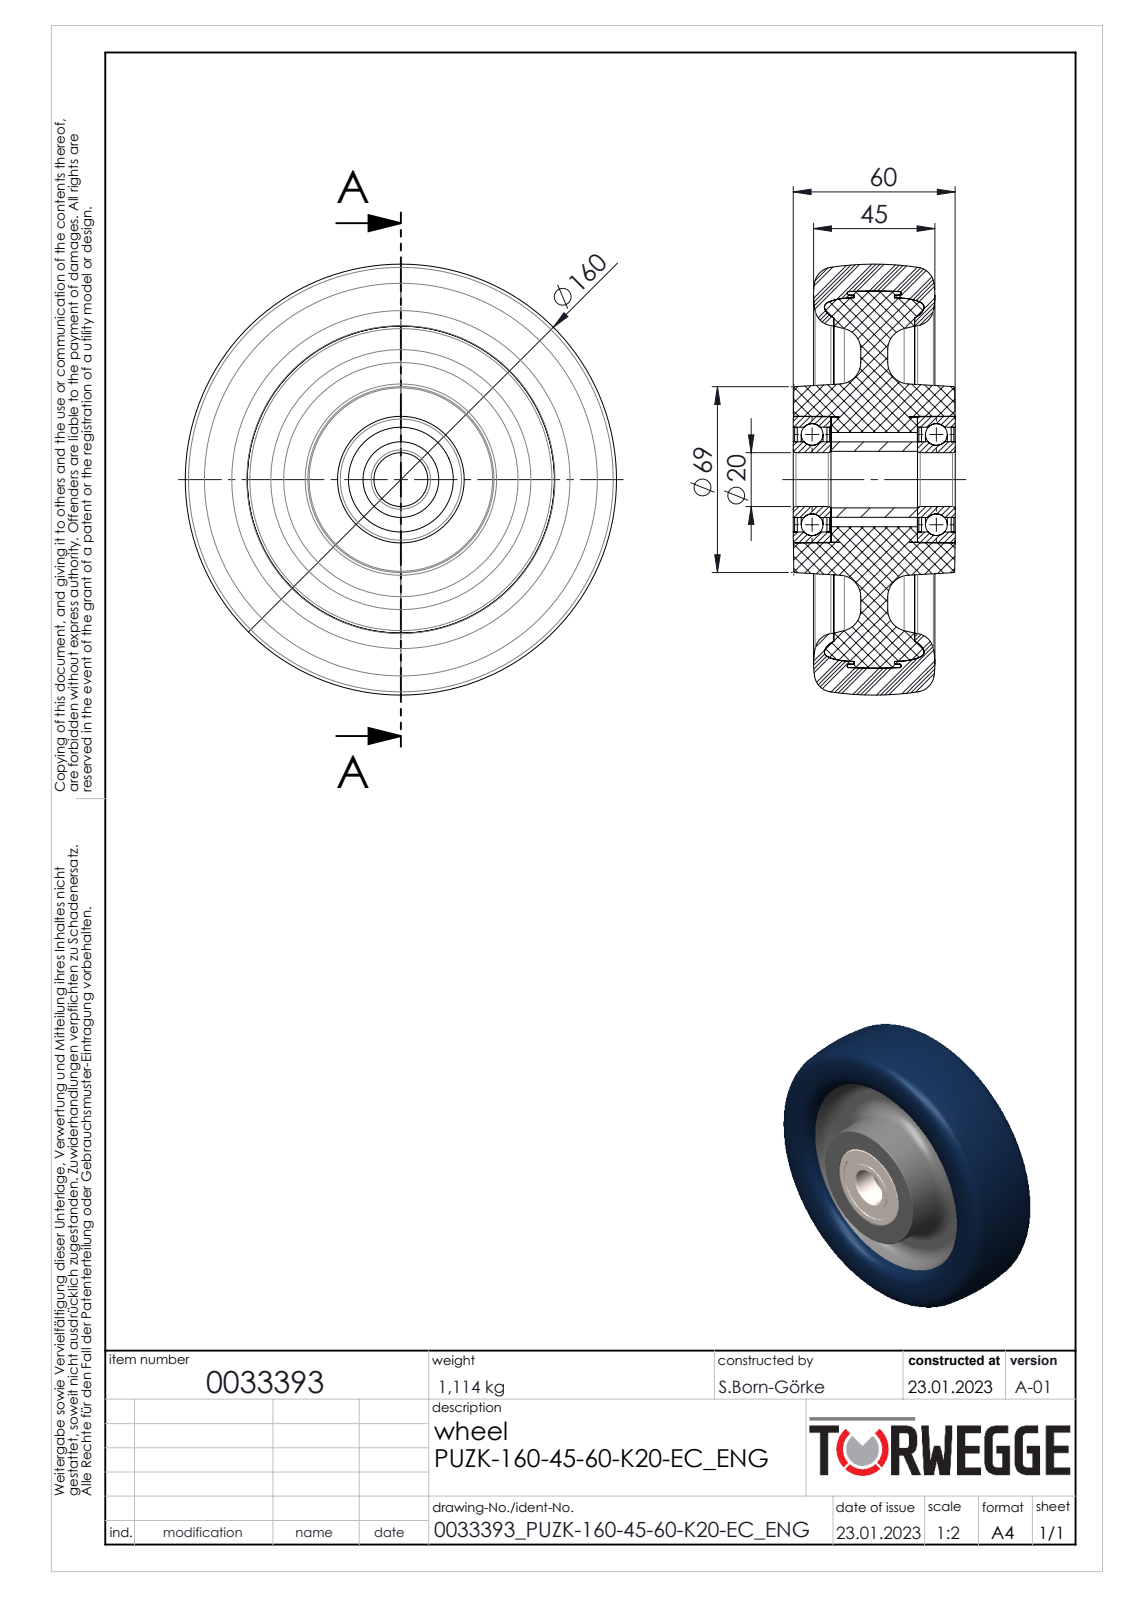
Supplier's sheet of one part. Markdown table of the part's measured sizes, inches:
| quantity | value |
| --- | --- |
| part name | 0033393 |
| STEP written by | SolidWorks 2020 (AUTOMOTIVE_DESIGN) |
| units | inches |
| bodies | 0 solids, 84 faces (12 planar, 14 cylindrical, 58 other) |
| overall size | 6.299 × 6.299 × 2.366 |
| round holes (diameter × count) | 0.787 × 1, 0.827 × 1, 1.531 × 1 |
| round bosses / shafts (diameter × count) | 1.106 × 1 |
| main face-to-face distances | 0.394, 0.787, 0.593, 0.986, 1.38, 1.774, 0.02, 2.346, 0.573, 0.967 |
